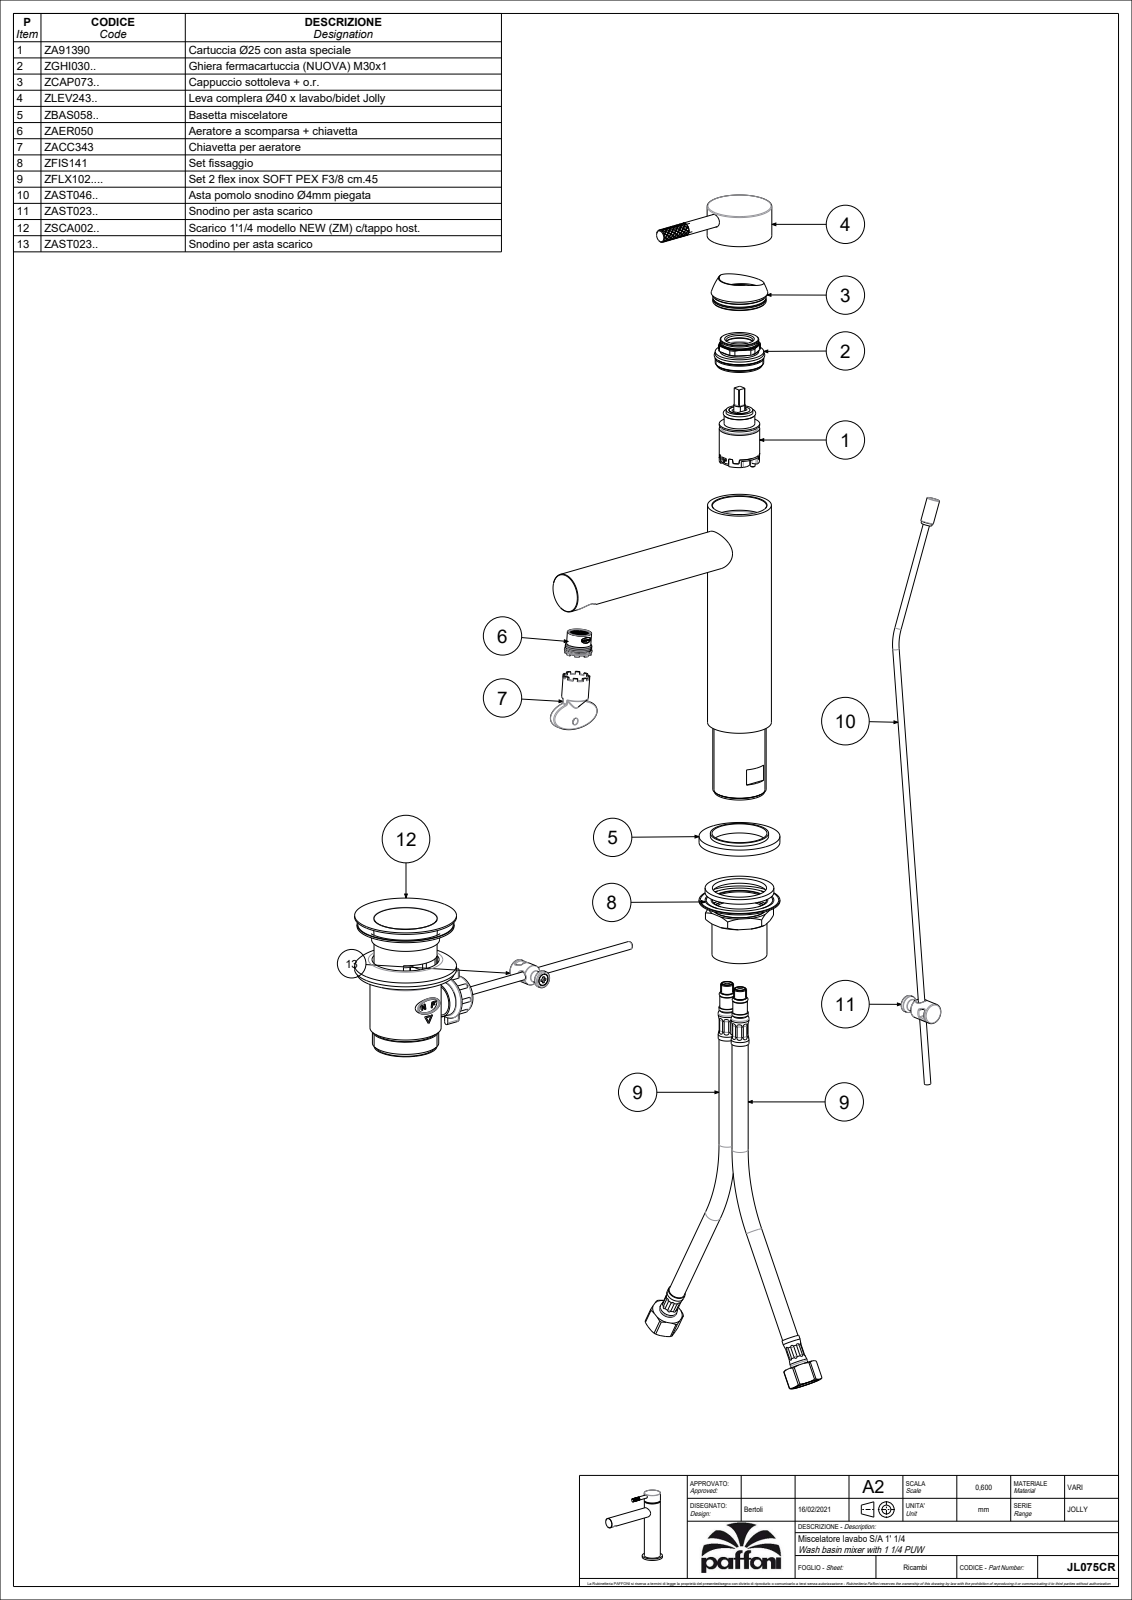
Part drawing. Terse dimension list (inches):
name: JL075CR
written by: CREO PARAMETRIC BY PTC INC, 2022124 (CONFIG_CONTROL_DESIGN)
unit: in
bodies: 7 solids, 3334 faces (1846 planar, 656 cylindrical, 832 other)
size: 6.941 × 6.673 × 1.969
volume: 8.1 in³; area: 121.3 in²
holes: 4× ⌀0.197, 3× ⌀0.276, 2× ⌀0.126, 2× ⌀0.177, 2× ⌀0.256, 2× ⌀0.37, 2× ⌀0.433, 1× ⌀0.118, 1× ⌀0.13, 1× ⌀0.165, 1× ⌀0.217, 1× ⌀0.319
bosses: 3× ⌀0.035, 2× ⌀0.433, 2× ⌀0.394, 2× ⌀0.354, 2× ⌀0.315, 2× ⌀0.157, 1× ⌀1.969, 1× ⌀1.693
rounds: 51× R0.005, 28× R0.118, 4× R0.024, 2× R0.217, 1× R0.294
face distances: 0.157, 0.079, 6.594, 6.437, 3.799, 3.642, 2.795, 4.382, 4.224, 0.583
hole spacings: 0.059, 0.265, 0.309, 0.351, 0.352, 0.367, 0.433, 0.609
